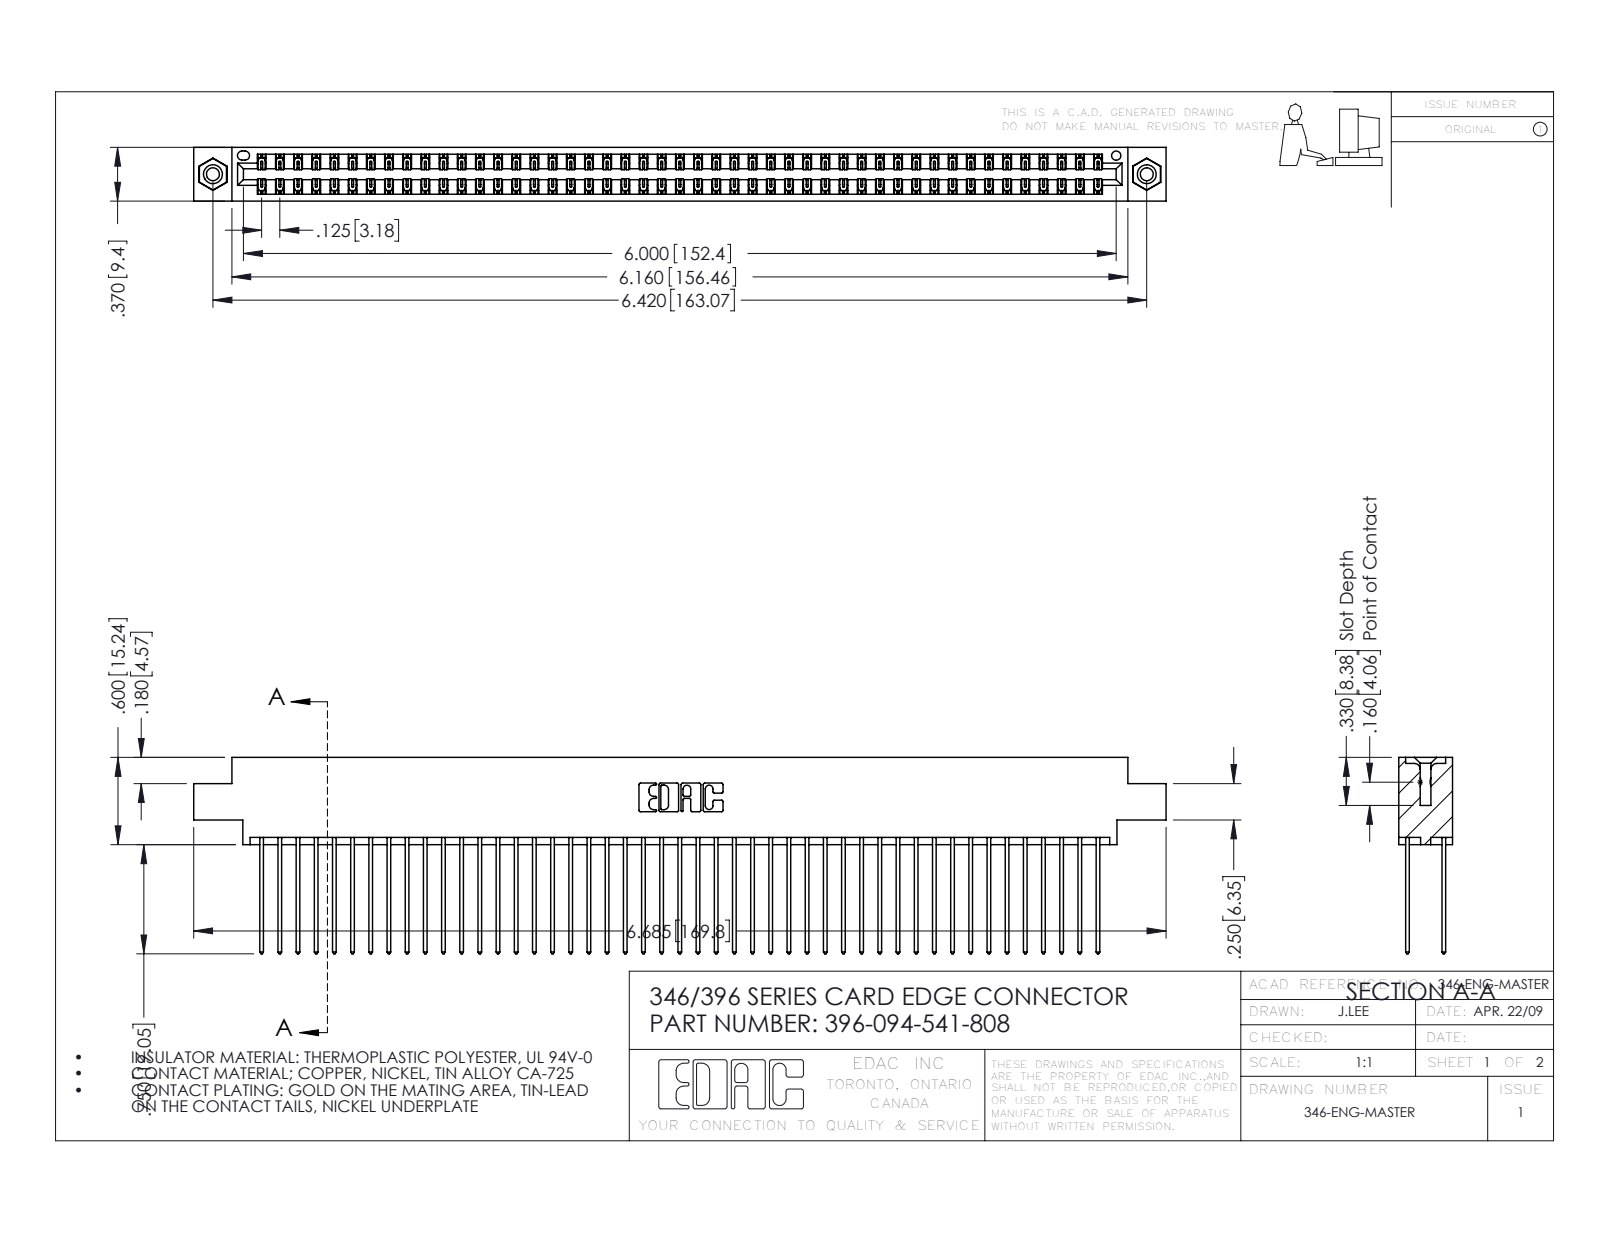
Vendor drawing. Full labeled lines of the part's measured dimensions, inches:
Part name (STEP PRODUCT): 346 Part_0.170 Offset - 0.156 Dia-TI; 345-292-001_345-293-141; 396-094-541-808; 345-250-001_345-250-003-102
STEP written by: SolidWorks 2016 (CONFIG_CONTROL_DESIGN)
Units: inches
Bodies: 97 solids, 5074 faces (3402 planar, 1656 cylindrical, 16 other)
Overall size (bounding box): 6.685 × 1.35 × 0.37
Volume: 1.036 in³ · Surface area: 40.61 in²
Round holes (diameter × count): ⌀0.089 ×2, ⌀0.125 ×2, ⌀0.156 ×2, ⌀0.064 ×1
Round bosses / shafts (diameter × count): ⌀0.155 ×2
Partial cylindrical surfaces — rounded edges, fillets, slot ends (radius × count): R0.006 ×141, R0.01 ×94, R0.01 ×22, R0.007 ×6, R0.031 ×6, R0.026 ×3, R0.014 ×2, R0.022 ×2
Main face-to-face distances: 0.048, 0.322, 0.25, 0.072, 0.298, 0.025, 0.37, 0.275, 0.225, 0.222
Hole centre spacings: 0.246, 6.211, 6.42
